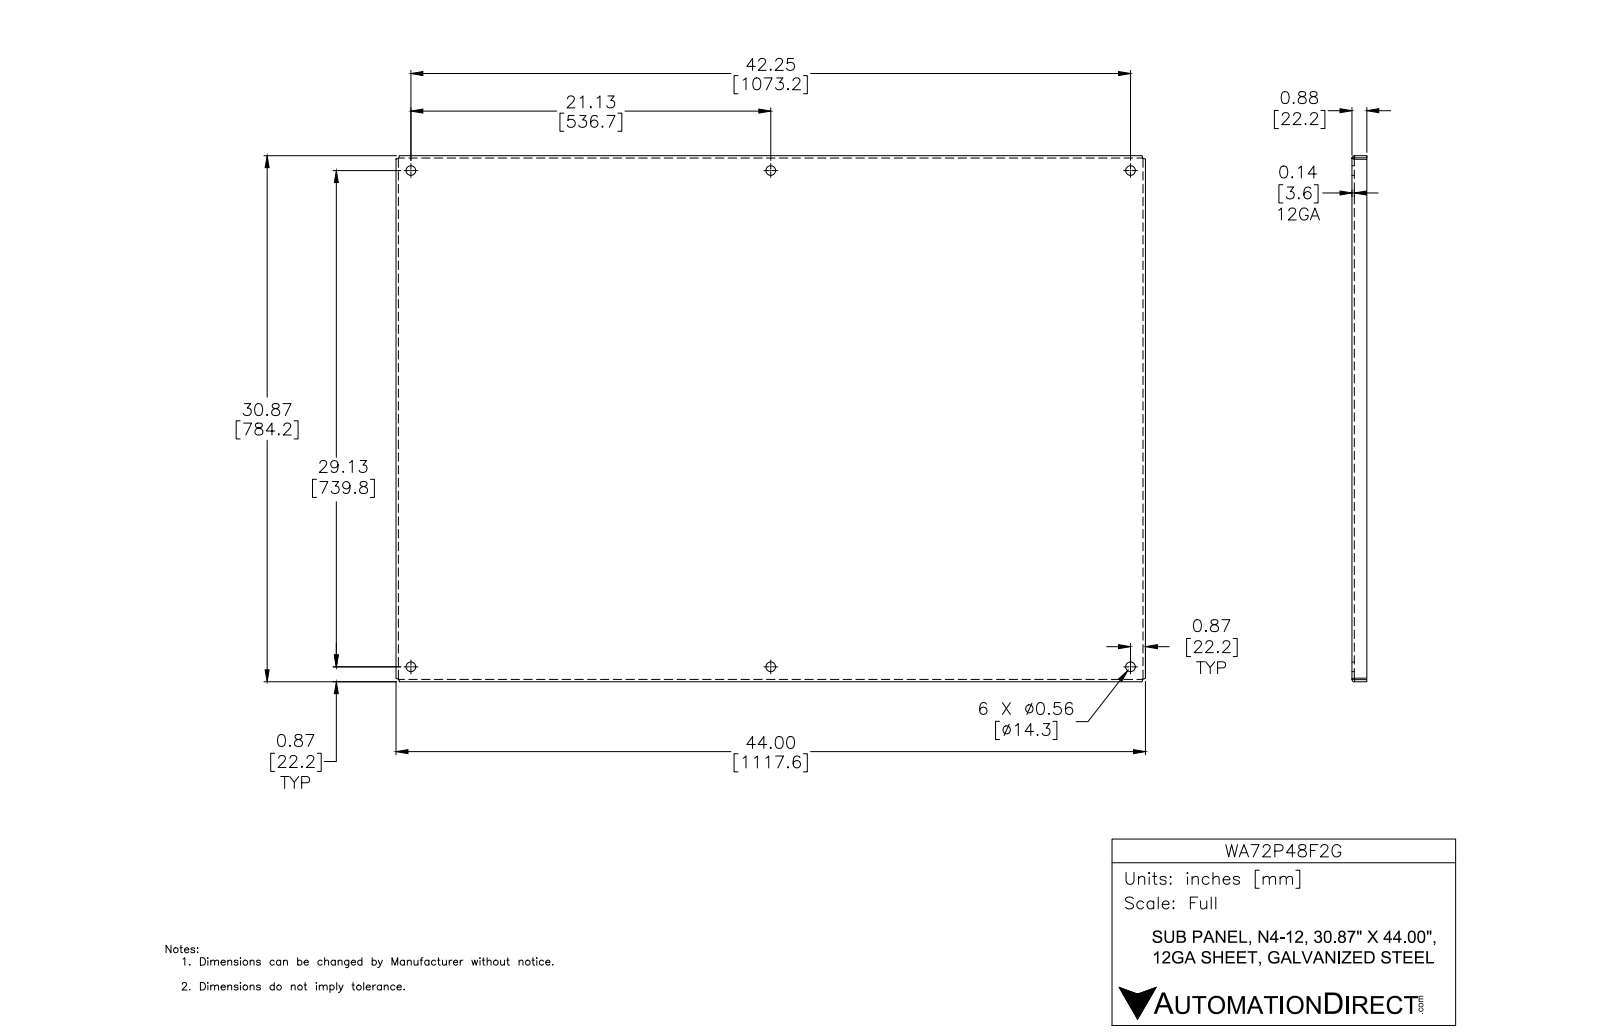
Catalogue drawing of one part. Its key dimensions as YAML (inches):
part_name: "WA_P_F_G"
step_written_by: "Autodesk Inventor 2012 (AUTOMOTIVE_DESIGN)"
units: inches
bodies: {solids: 1, faces: 44, planar: 22, cylindrical: 14, other: 8}
overall_size: [44, 30.88, 0.875]
volume: 182.9
surface_area: 2947
round_holes:
  - {diameter: 0.563, count: 6}
partial_cylinders:
  - {radius: 0.016, count: 4}
  - {radius: 0.141, count: 4}
face_to_face_distances: [0.125, 0.125, 43.875, 30.755, 30.88, 30.63, 30.755, 44, 43.75, 0.75]
hole_center_spacings: [35.984, 21.125, 21.125, 29.13, 42.25, 51.319, 29.13, 35.983]
